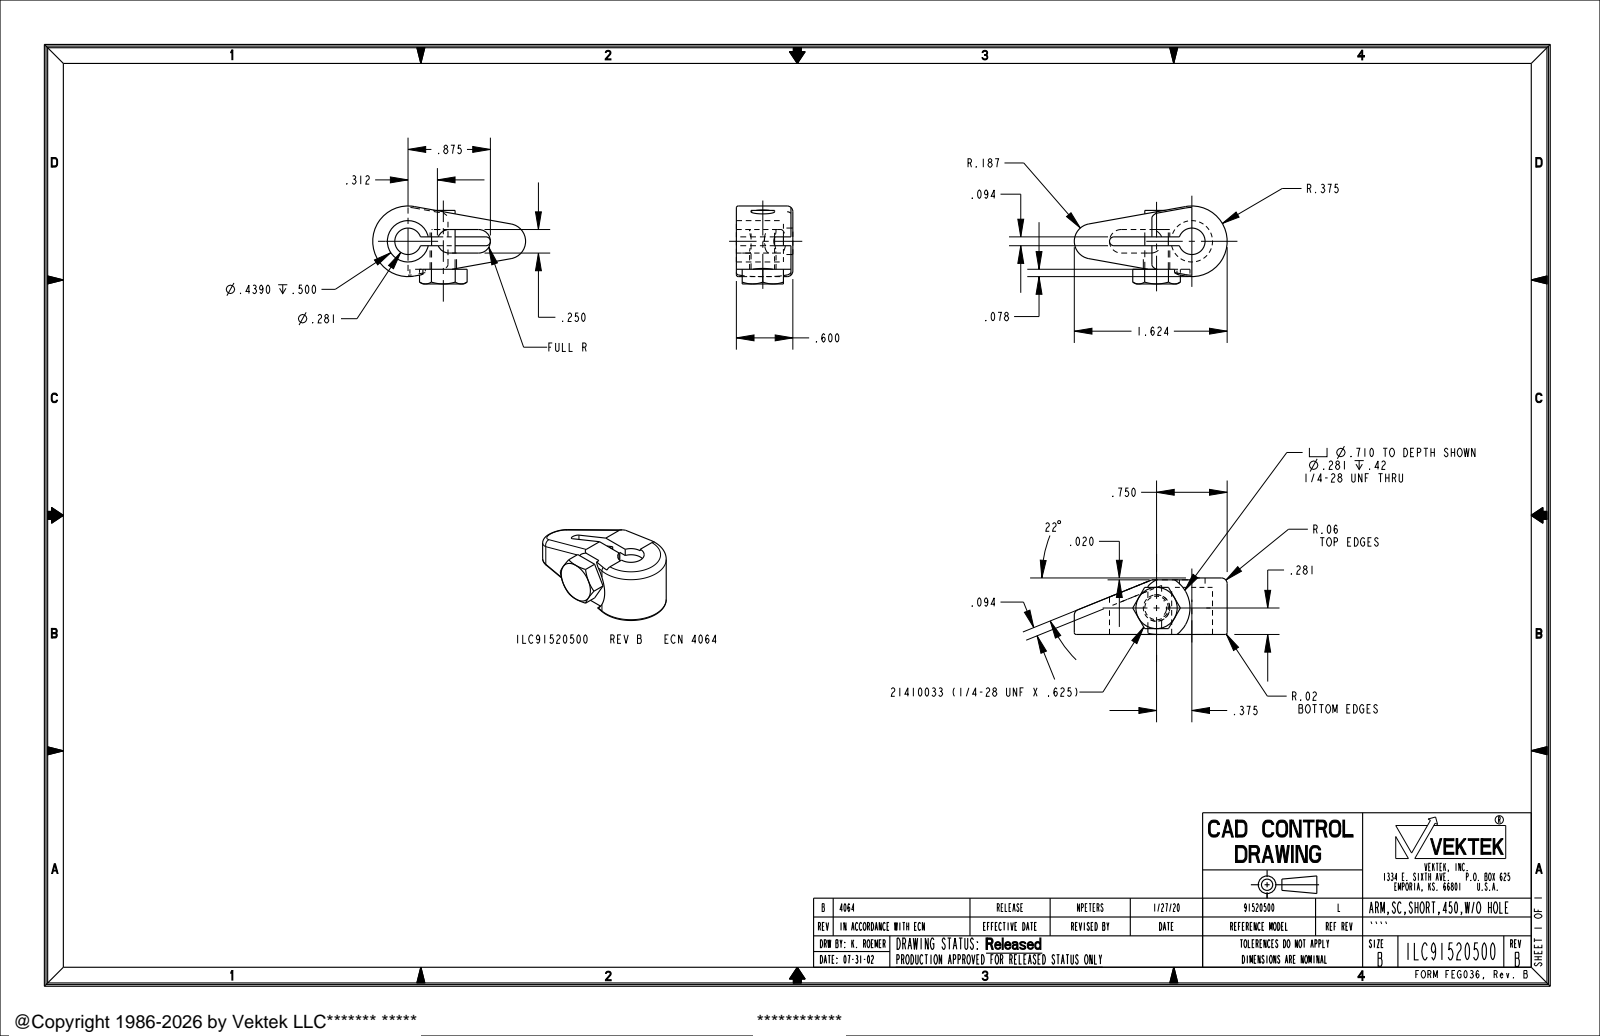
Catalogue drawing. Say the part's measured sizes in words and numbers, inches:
The part is named "ILC91520500". Its 3-D file was written by "PRO/ENGINEER BY PARAMETRIC TECHNOLOGY CORPORATION, 2013320 (AUTOMOTIVE_DESIGN)". It is 1 solid with 63 faces: 28 planar, 25 cylindrical and 10 other. Overall it measures 1.624 by 0.828 by 0.6 inches. Its volume is 0.34 cubic inches and its surface area 5.646 square inches. Round holes: 2 of diameter 0.281, 1 of diameter 0.439. Round bosses or shafts: 1 of diameter 0.25. Partial cylindrical surfaces (rounded edges, fillets, slot ends): 4 of radius 0.06, 2 of radius 0.02, 2 of radius 0.125, 1 of radius 0.047, 1 of radius 0.106, 1 of radius 0.187, 1 of radius 0.355, 1 of radius 0.375. The main face-to-face distances are 0.5, 0.58, 0.078, 0.172, 0.094, 0.156, 0.578, 0.422, 0.6, 0.02.
